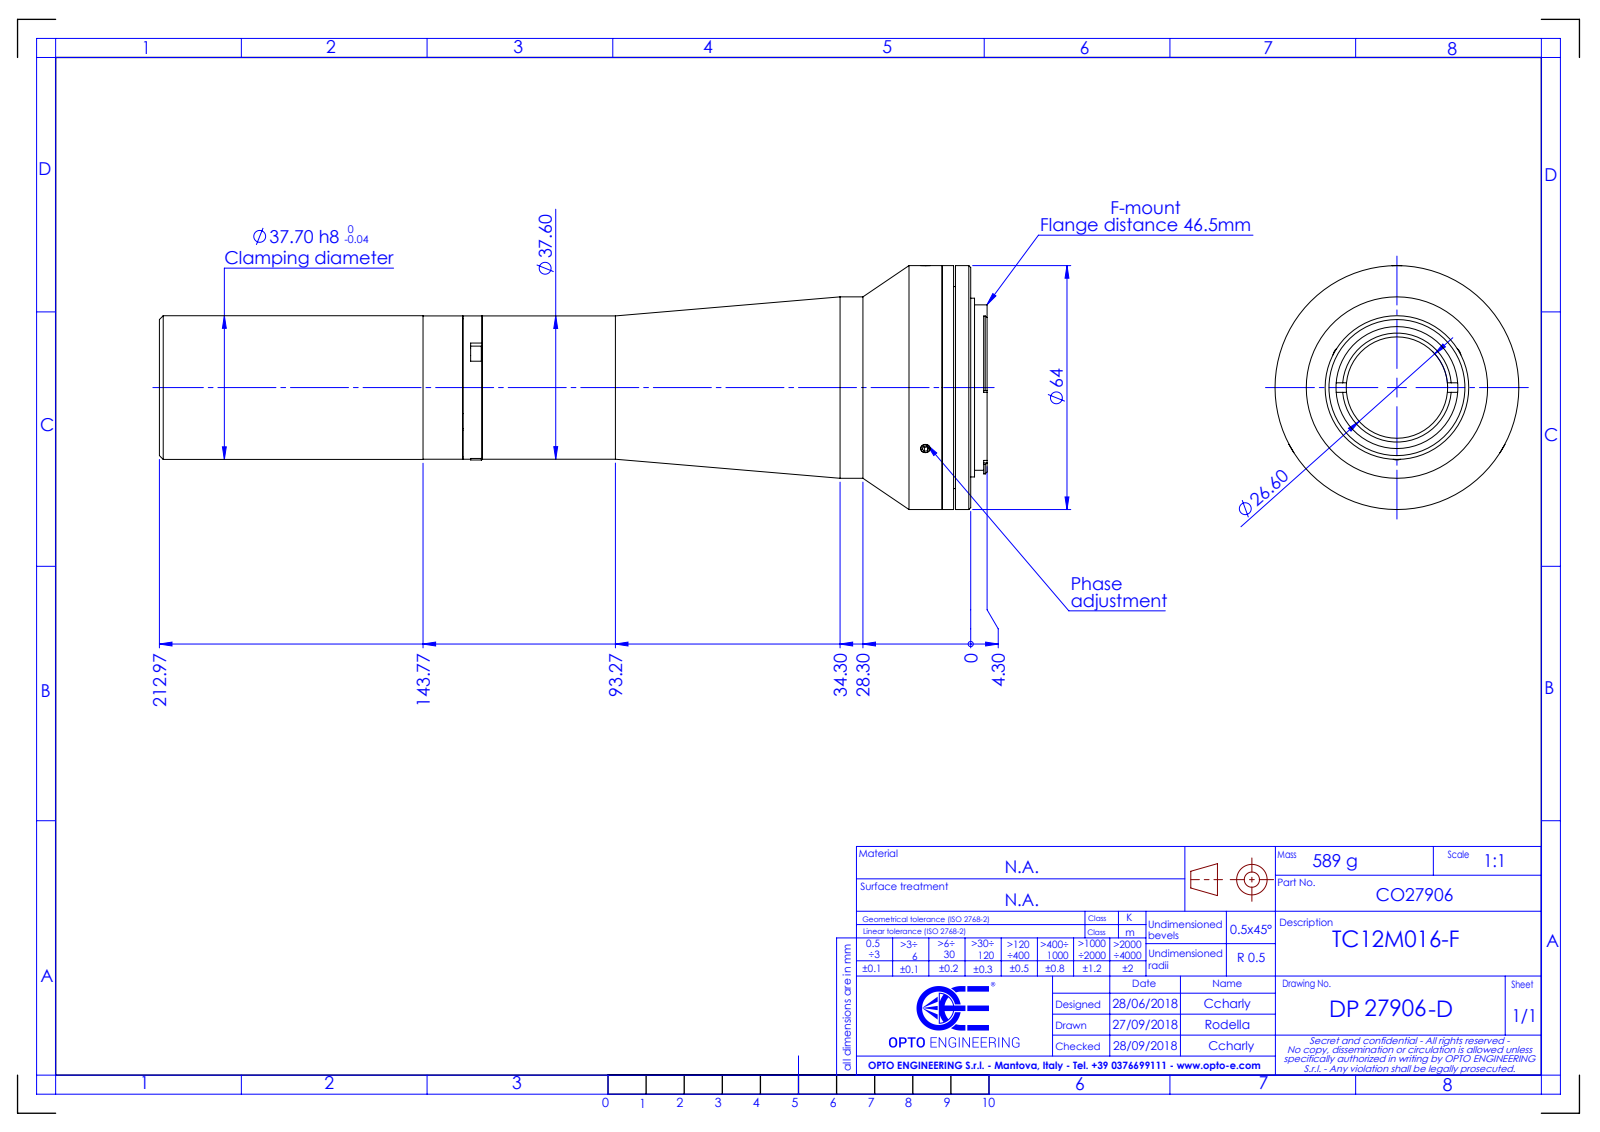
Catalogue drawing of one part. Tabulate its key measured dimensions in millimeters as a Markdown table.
| quantity | value |
| --- | --- |
| part name | DP27906_TC12M016-F |
| STEP written by | SolidWorks 2021 (CONFIG_CONTROL_DESIGN) |
| units | millimeters |
| bodies | 0 solids, 136 faces (59 planar, 47 cylindrical, 30 other) |
| overall size | 217.27 × 64 × 64 |
| round holes (diameter × count) | 26.6 × 1, 32 × 1, 41 × 1, 42 × 1 |
| round bosses / shafts (diameter × count) | 5.5 × 3, 64 × 1, 47.6 × 1, 46.9 × 1, 43.4 × 1, 37.7 × 1, 37.6 × 1 |
| partial cylindrical surfaces (radius × count) | 0.5 × 6, 1.15 × 2, 22.65 × 1 |
| main face-to-face distances | 7.5, 3, 123.77, 120.77, 128.27, 4.5, 124.27, 3.5, 0.5, 4 |
